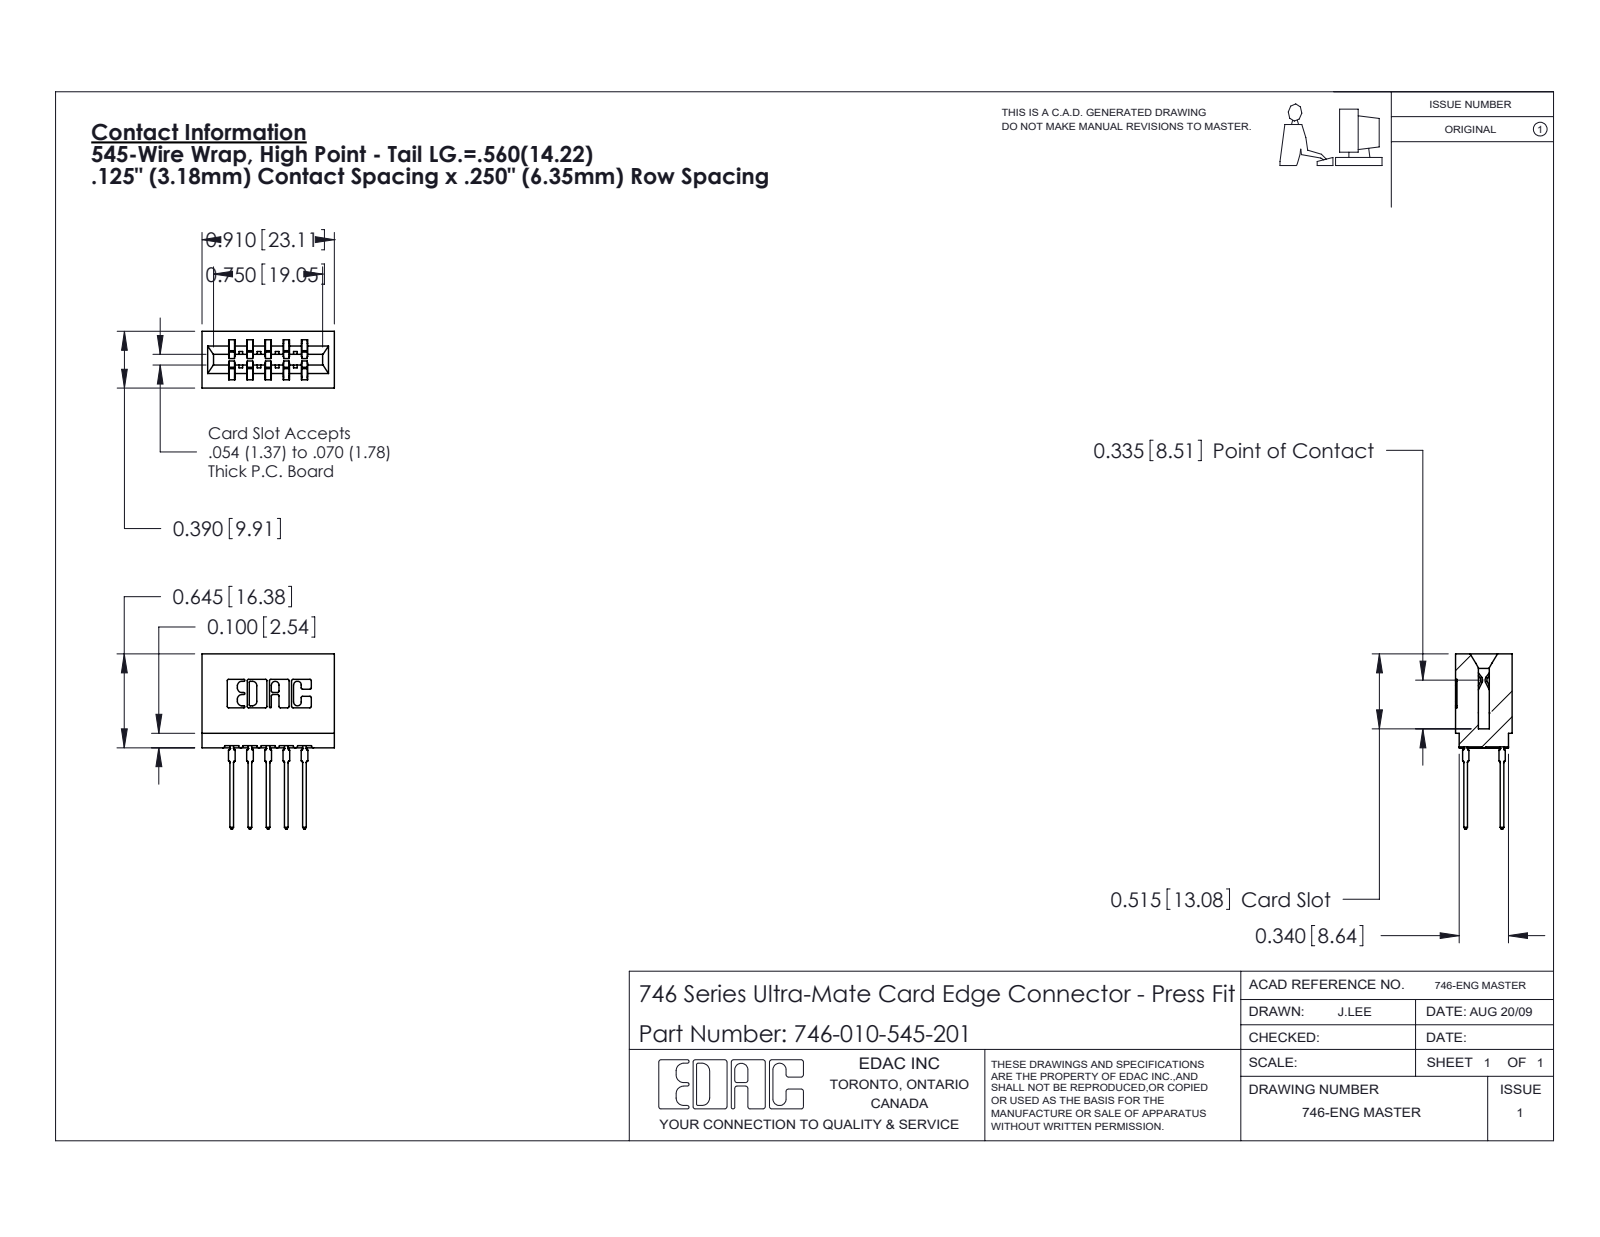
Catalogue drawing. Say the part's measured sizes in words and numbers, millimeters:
The part is named "746-292-001_545; 746 Part_.515 Slot Depth - 01; 746-010-545-201". Its 3-D file was written by "SolidWorks 2020 (CONFIG_CONTROL_DESIGN)". It is 11 solids with 992 faces: 515 planar, 217 cylindrical and 260 other. Overall it measures 30.6 by 23.1 by 9.9 millimeters. Its volume is 2 750 cubic millimeters and its surface area 3 834 square millimeters. Partial cylindrical surfaces (rounded edges, fillets, slot ends): 22 of radius 0.3, 20 of radius 0.5, 8 of radius 0.1, 8 of radius 0.3, 6 of radius 0.2, 6 of radius 0.4, 6 of radius 0.8, 3 of radius 0.7. The main face-to-face distances are 6.4, 1.4, 8.5, 1.1, 3.2, 3.2, 2.1, 9.9, 0.6, 7.8.
